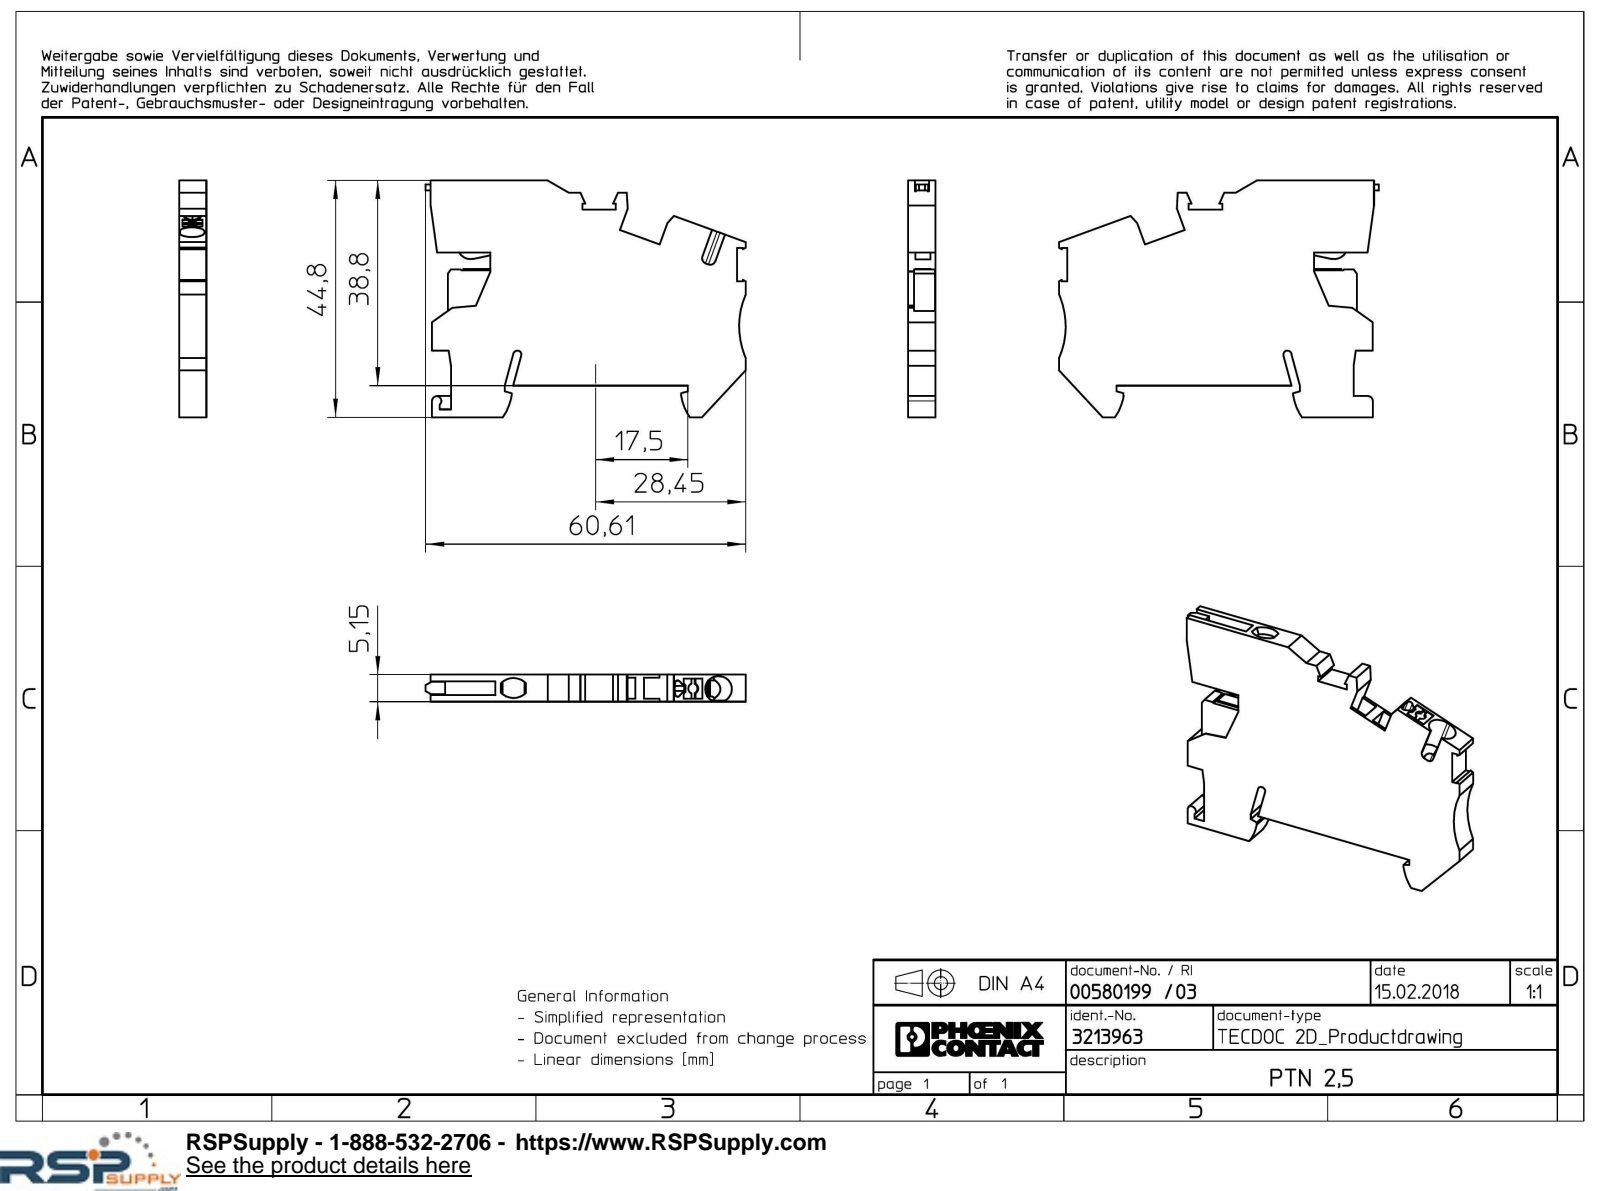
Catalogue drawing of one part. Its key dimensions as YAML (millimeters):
part_name: "PTN_2.5-select"
step_written_by: "Creo Elements/Direct Modeling 18.1I 14-Aug-2016 (C) Parametric Technology GmbH (AUTOMOTIVE_DESIGN)"
units: millimeters
bodies: {solids: 1, faces: 154, planar: 128, cylindrical: 18, other: 8}
overall_size: [60.6, 44.8, 5.15]
volume: 9754
surface_area: 6162
partial_cylinders:
  - {radius: 1, count: 3}
  - {radius: 2.4, count: 3}
  - {radius: 0.5, count: 2}
  - {radius: 3.3, count: 2}
  - {radius: 9.5, count: 2}
  - {radius: 0.7, count: 1}
  - {radius: 0.8, count: 1}
  - {radius: 0.9, count: 1}
face_to_face_distances: [5.15, 6, 4, 0.57, 4.58, 0.58, 4.57, 3.48, 38.8, 8.01]
